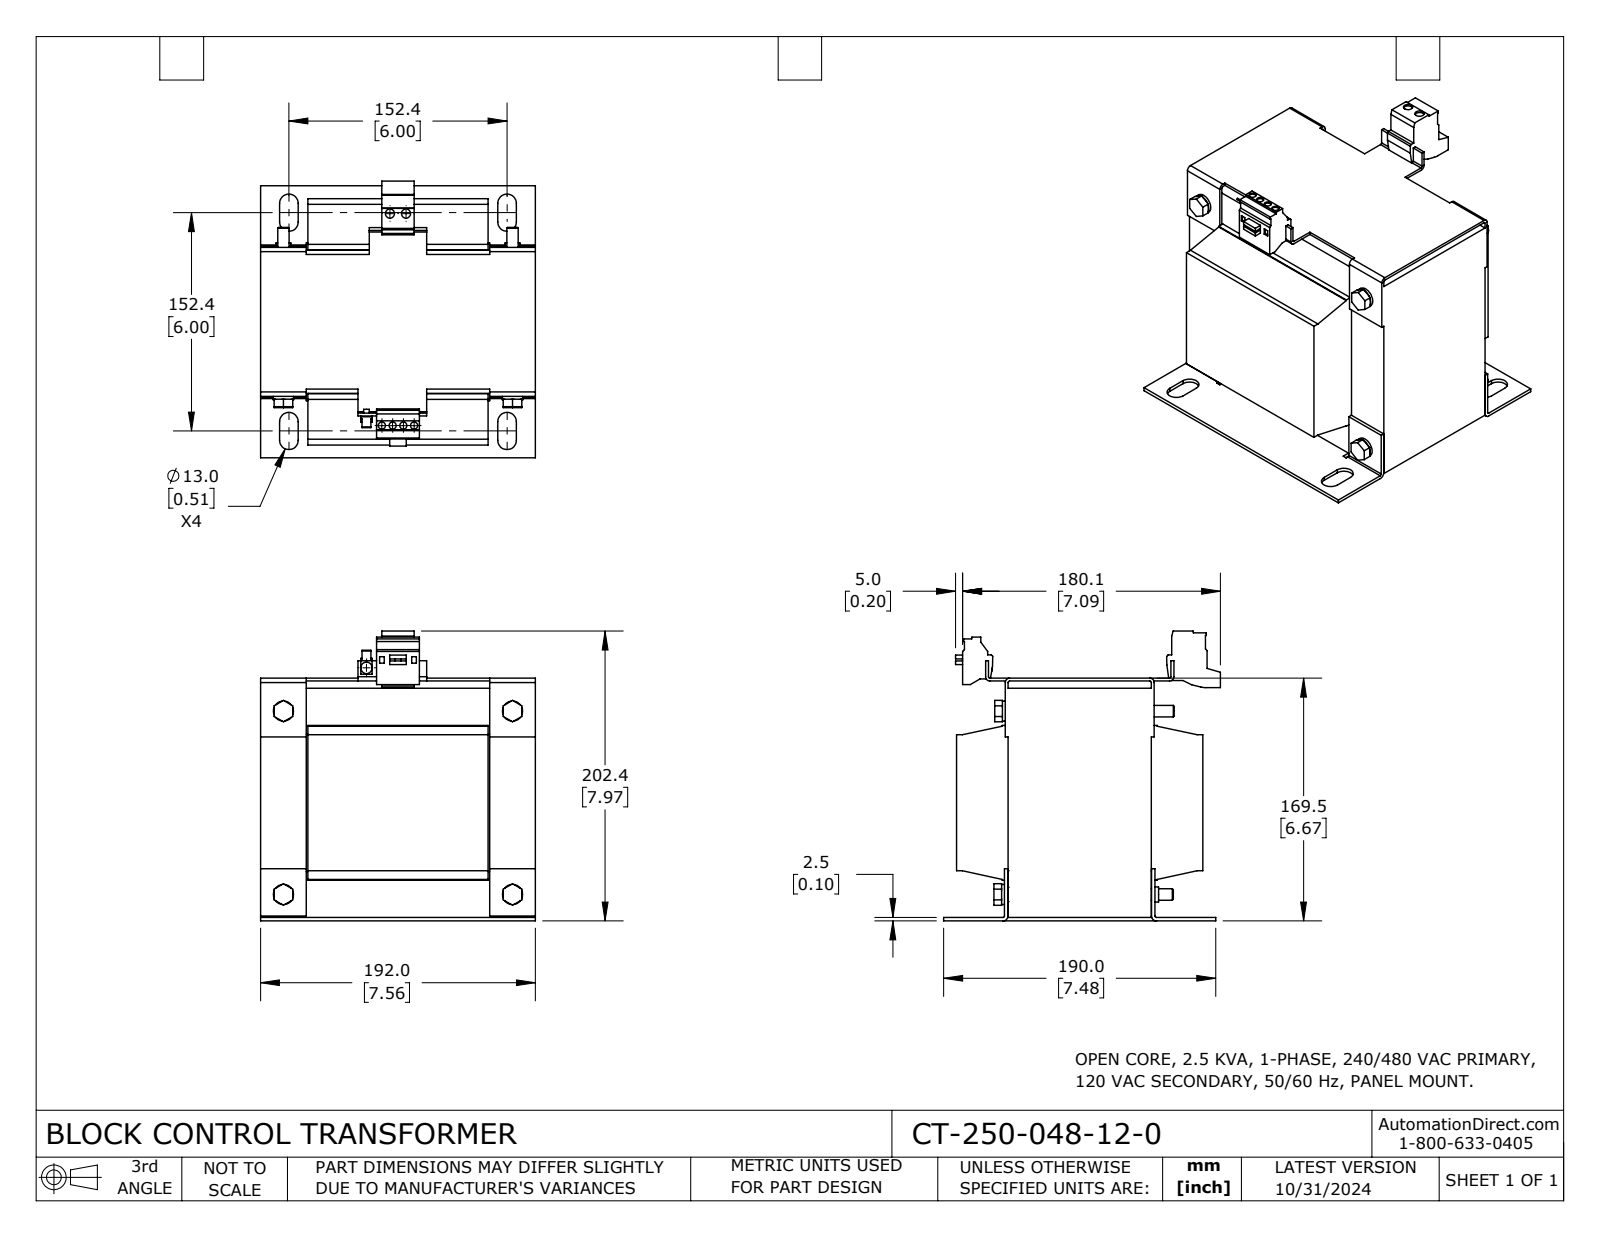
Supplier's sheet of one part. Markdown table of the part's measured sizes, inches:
| quantity | value |
| --- | --- |
| part name | CT-250-048-12-0 |
| STEP written by | SolidWorks 2023 (CONFIG_CONTROL_DESIGN) |
| units | inches |
| bodies | 1 solid, 390 faces (301 planar, 81 cylindrical, 8 other) |
| overall size | 7.969 × 7.61 × 7.559 |
| volume | 252.8 in³ |
| surface area | 514.8 in² |
| round holes (diameter × count) | 0.197 × 4, 0.252 × 2 |
| round bosses / shafts (diameter × count) | 0.315 × 5, 0.551 × 4, 0.413 × 2, 0.394 × 2, 0.157 × 1 |
| partial cylindrical surfaces (radius × count) | 0.256 × 8, 0.039 × 6, 0.118 × 4, 0.138 × 2, 0.591 × 1 |
| main face-to-face distances | 6.299, 1.299, 6.26, 1.26, 0.098, 0.079, 1.417, 5.354, 5.039, 0.039 |
| hole center spacings | 0.295, 0.591, 5.827, 5.831, 5.839, 5.865, 0.443, 0.886 |
